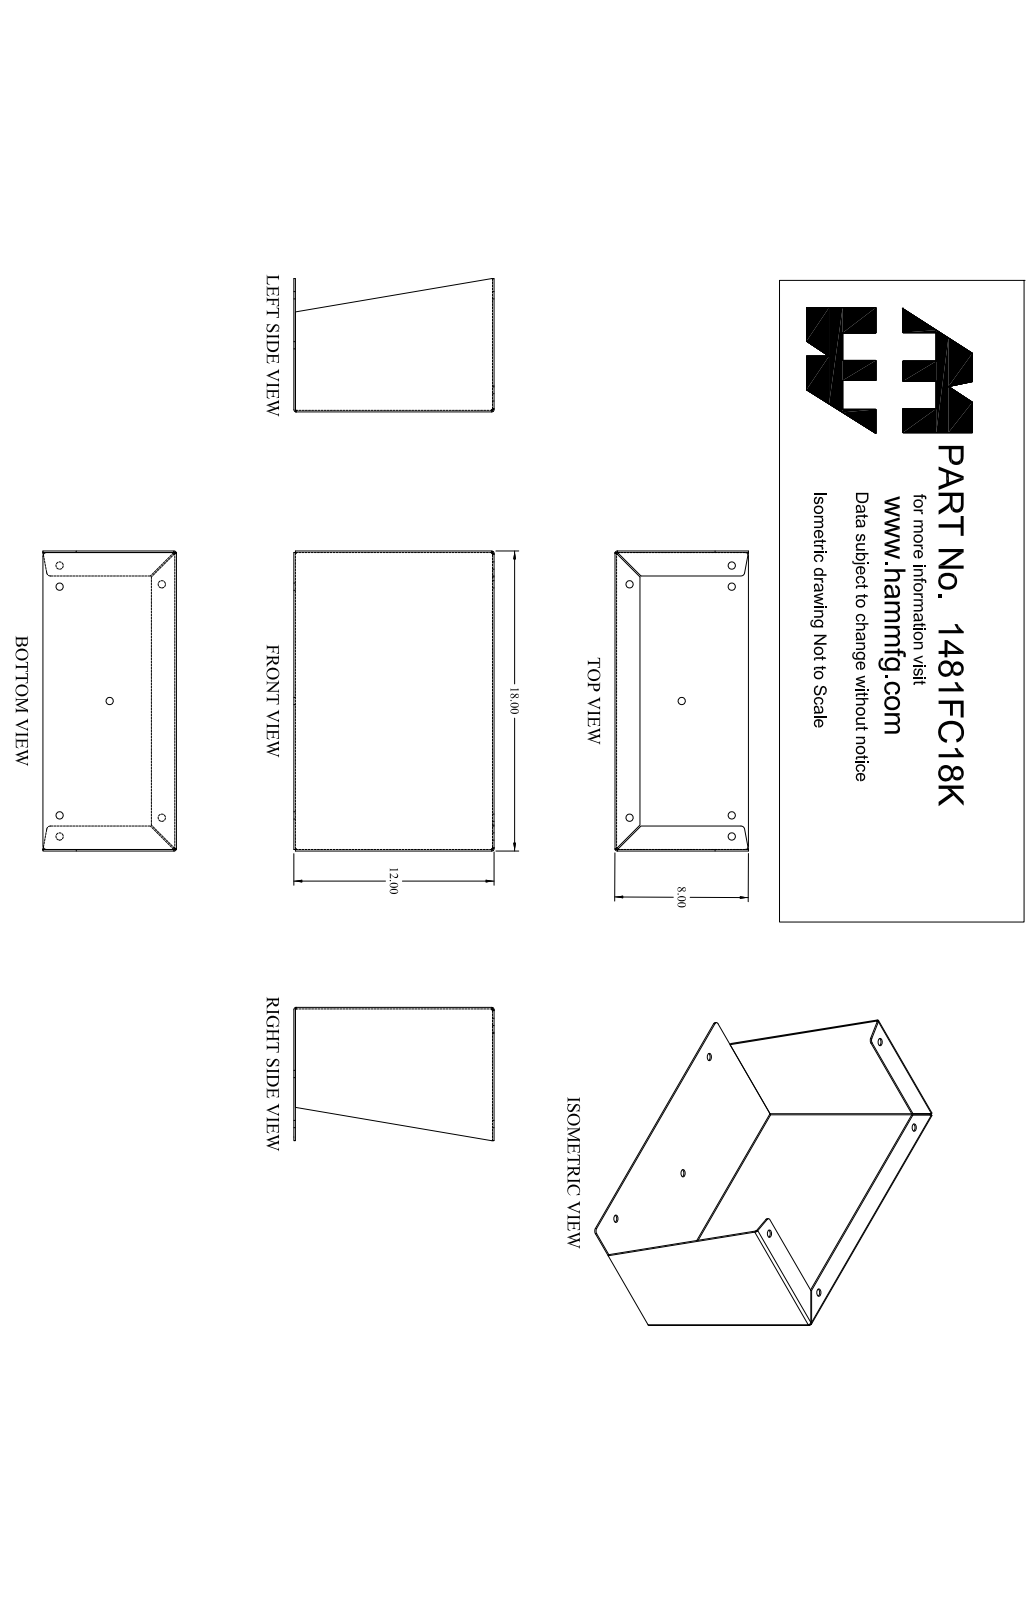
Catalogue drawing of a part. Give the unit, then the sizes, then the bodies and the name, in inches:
Units: inches
Overall size (bounding box): 18 × 12 × 8
Round holes (diameter × count): ⌀0.437 ×7
Partial cylindrical surfaces — rounded edges, fillets, slot ends (radius × count): R0.048 ×6, R0.143 ×6, R0.22 ×4
Main face-to-face distances: 0.095, 17.905, 0.095, 18, 17.81, 11.81, 11.905, 11.905, 12, 1.405
Hole centre spacings: 6.126, 6.227, 7.487, 7.666, 15.152, 1.266, 1.266, 8.661
Volume: 53.18 in³ · Surface area: 1 131 in²
Bodies: 1 solid, 78 faces (42 planar, 30 cylindrical, 6 other)
Part name (STEP PRODUCT): 1481FC18K_Default
STEP written by: SolidWorks 2019 (CONFIG_CONTROL_DESIGN)
